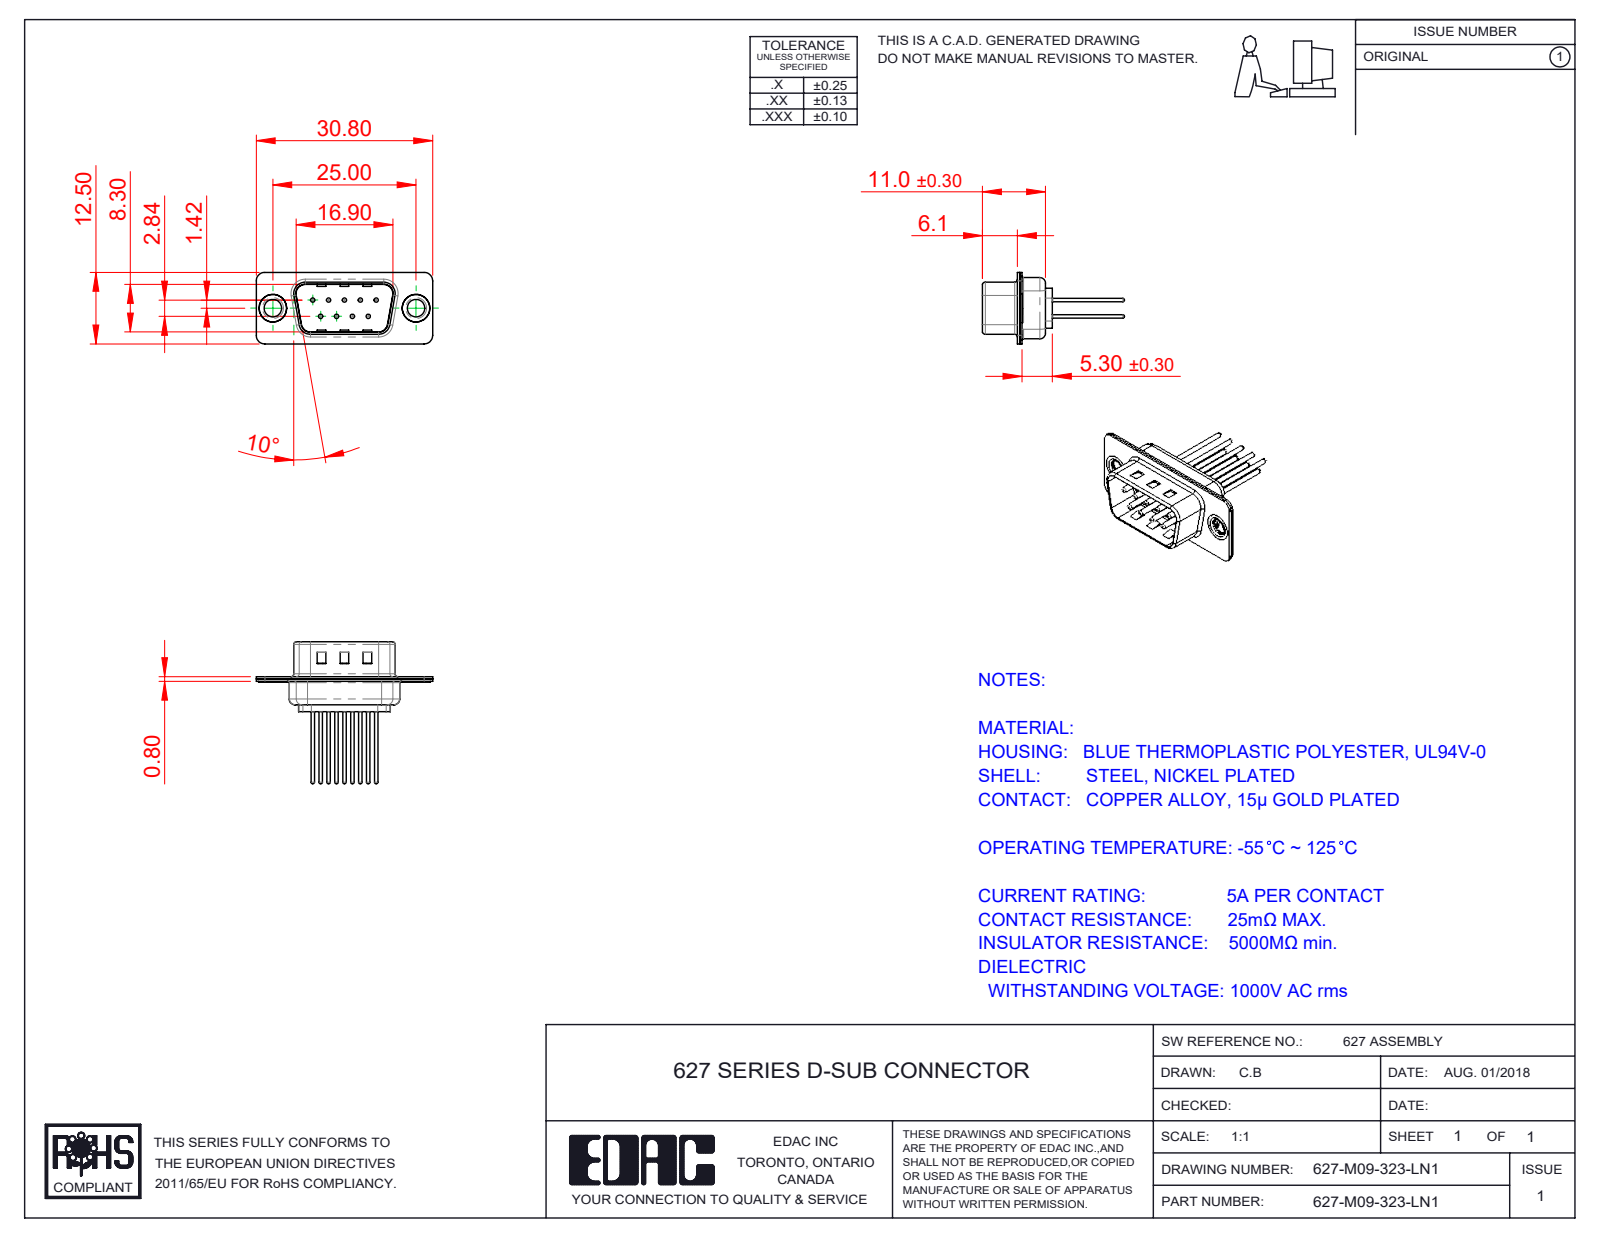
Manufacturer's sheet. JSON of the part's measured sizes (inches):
{"part_name": "627M Shell Rear_09 Contacts; 627-M09-323-LN1; 627M Housing_09 Contacts; 627M Contact Row 2_23 (+3 more)", "step_written_by": "SolidWorks 2020 (CONFIG_CONTROL_DESIGN)", "units": "inches", "bodies": {"solids": 14, "faces": 611, "planar": 170, "cylindrical": 239, "other": 202}, "overall_size": [1.213, 0.975, 0.492], "volume_in3": 0.076, "surface_area_in2": 5.495, "round_holes": [[0.03, 9], [0.063, 9], [0.079, 9], [0.12, 2], [0.157, 2], [0.189, 2]], "round_bosses_or_shafts": [[0.059, 9], [0.024, 9], [0.197, 2], [0.193, 2], [0.14, 2]], "partial_cylinders_radius": [[0.059, 16], [0.079, 12], [0.02, 8], [0.063, 8], [0.01, 4], [0.024, 4], [0.026, 4], [0.035, 4]], "face_to_face_distances": [0.016, 0.031, 0.374, 0.358, 0.343, 0.026, 0.39, 0.047, 0.24, 0.209], "hole_center_spacings": [0.124, 0.109, 0.218, 0.198, 0.198, 0.327, 0.28, 0.294]}
